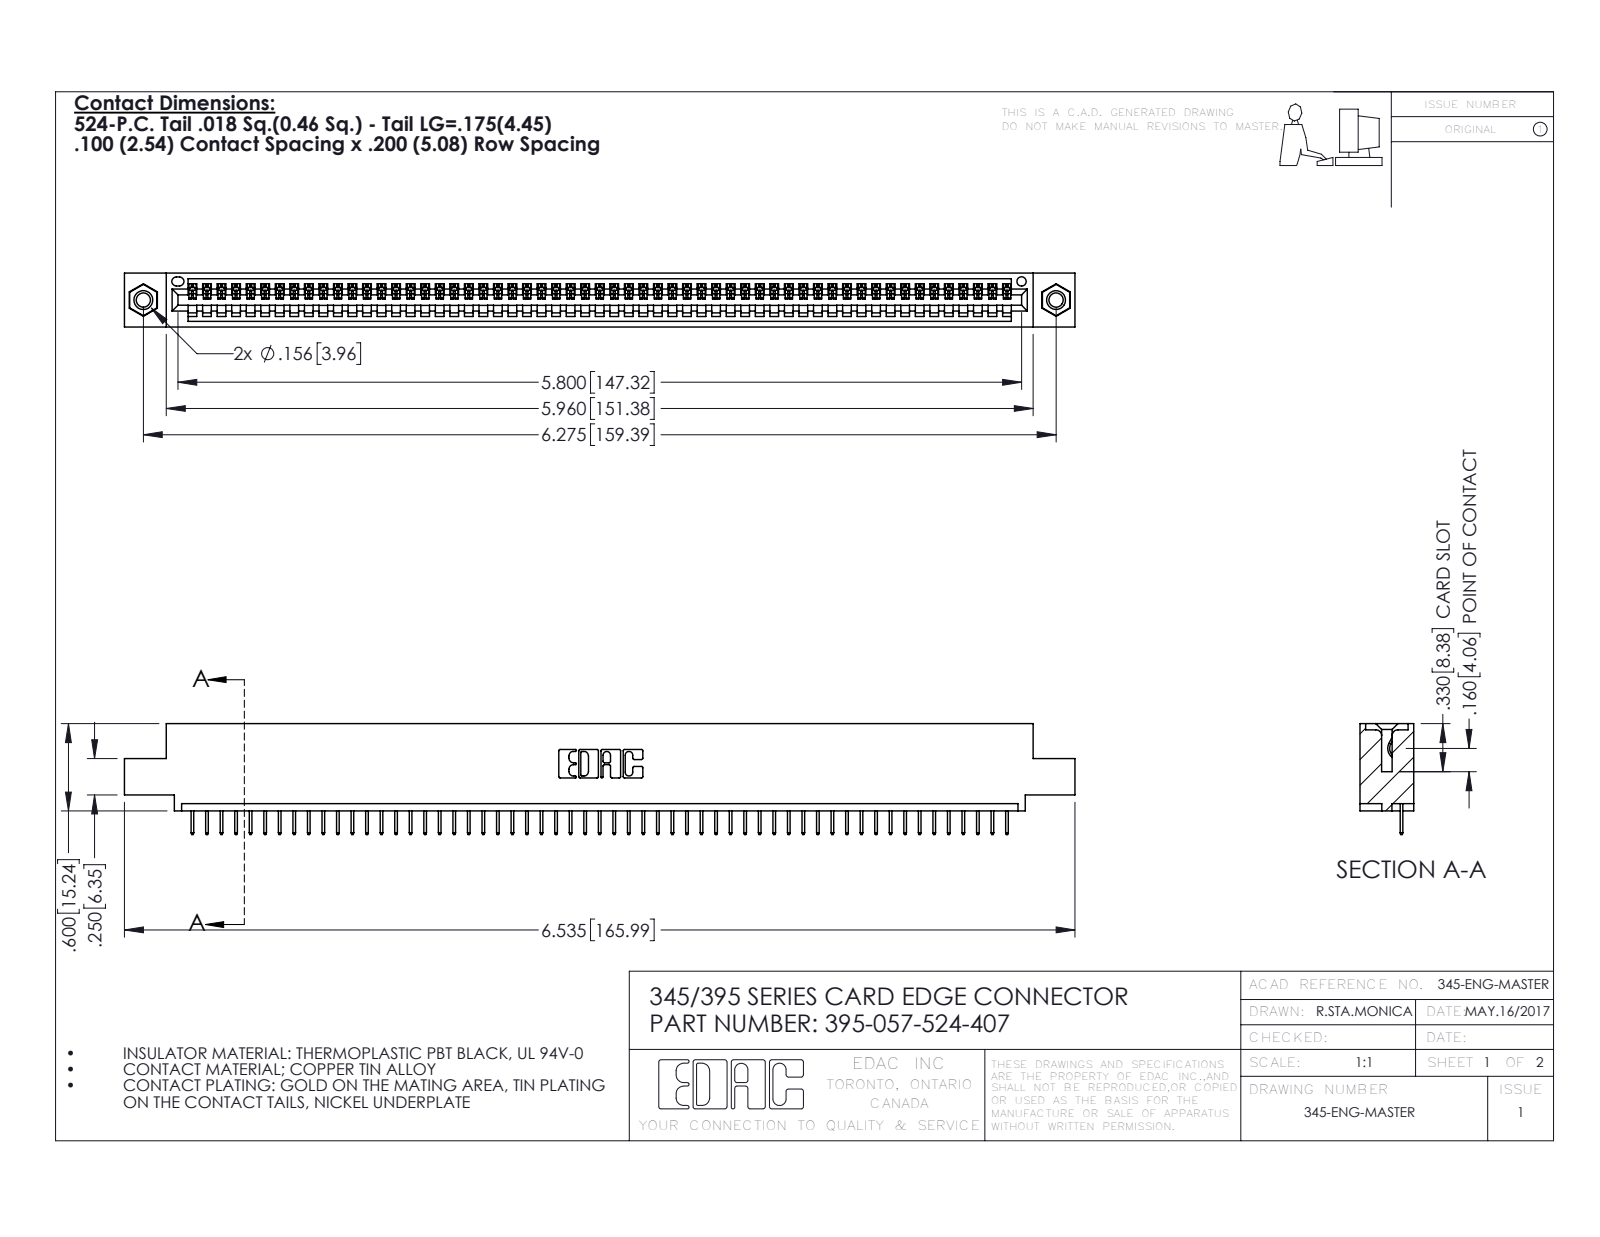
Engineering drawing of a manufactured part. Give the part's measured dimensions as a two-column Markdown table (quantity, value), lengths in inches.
| quantity | value |
| --- | --- |
| part name | 395-057-524-407; 345 Part_0.110 Offset - 0.156 Dia-TI; 345-250-001_345-250-005-103; 345-292-001_345-293-124 |
| STEP written by | SolidWorks 2016 (CONFIG_CONTROL_DESIGN) |
| units | inches |
| bodies | 60 solids, 3724 faces (2738 planar, 970 cylindrical, 16 other) |
| overall size | 6.535 × 0.762 × 0.37 |
| volume | 0.951 in³ |
| surface area | 31.46 in² |
| round holes (diameter × count) | 0.098 × 2, 0.125 × 2, 0.156 × 2, 0.064 × 1 |
| round bosses / shafts (diameter × count) | 0.155 × 2 |
| partial cylindrical surfaces (radius × count) | 0.006 × 114, 0.01 × 22, 0.007 × 6, 0.031 × 6, 0.026 × 3, 0.031 × 2, 0.04 × 2, 0.014 × 1 |
| main face-to-face distances | 0.072, 0.298, 0.37, 0.2, 0.098, 0.272, 0.025, 0.225, 0.072, 0.149 |
| hole center spacings | 0.27, 6.039, 6.275 |
